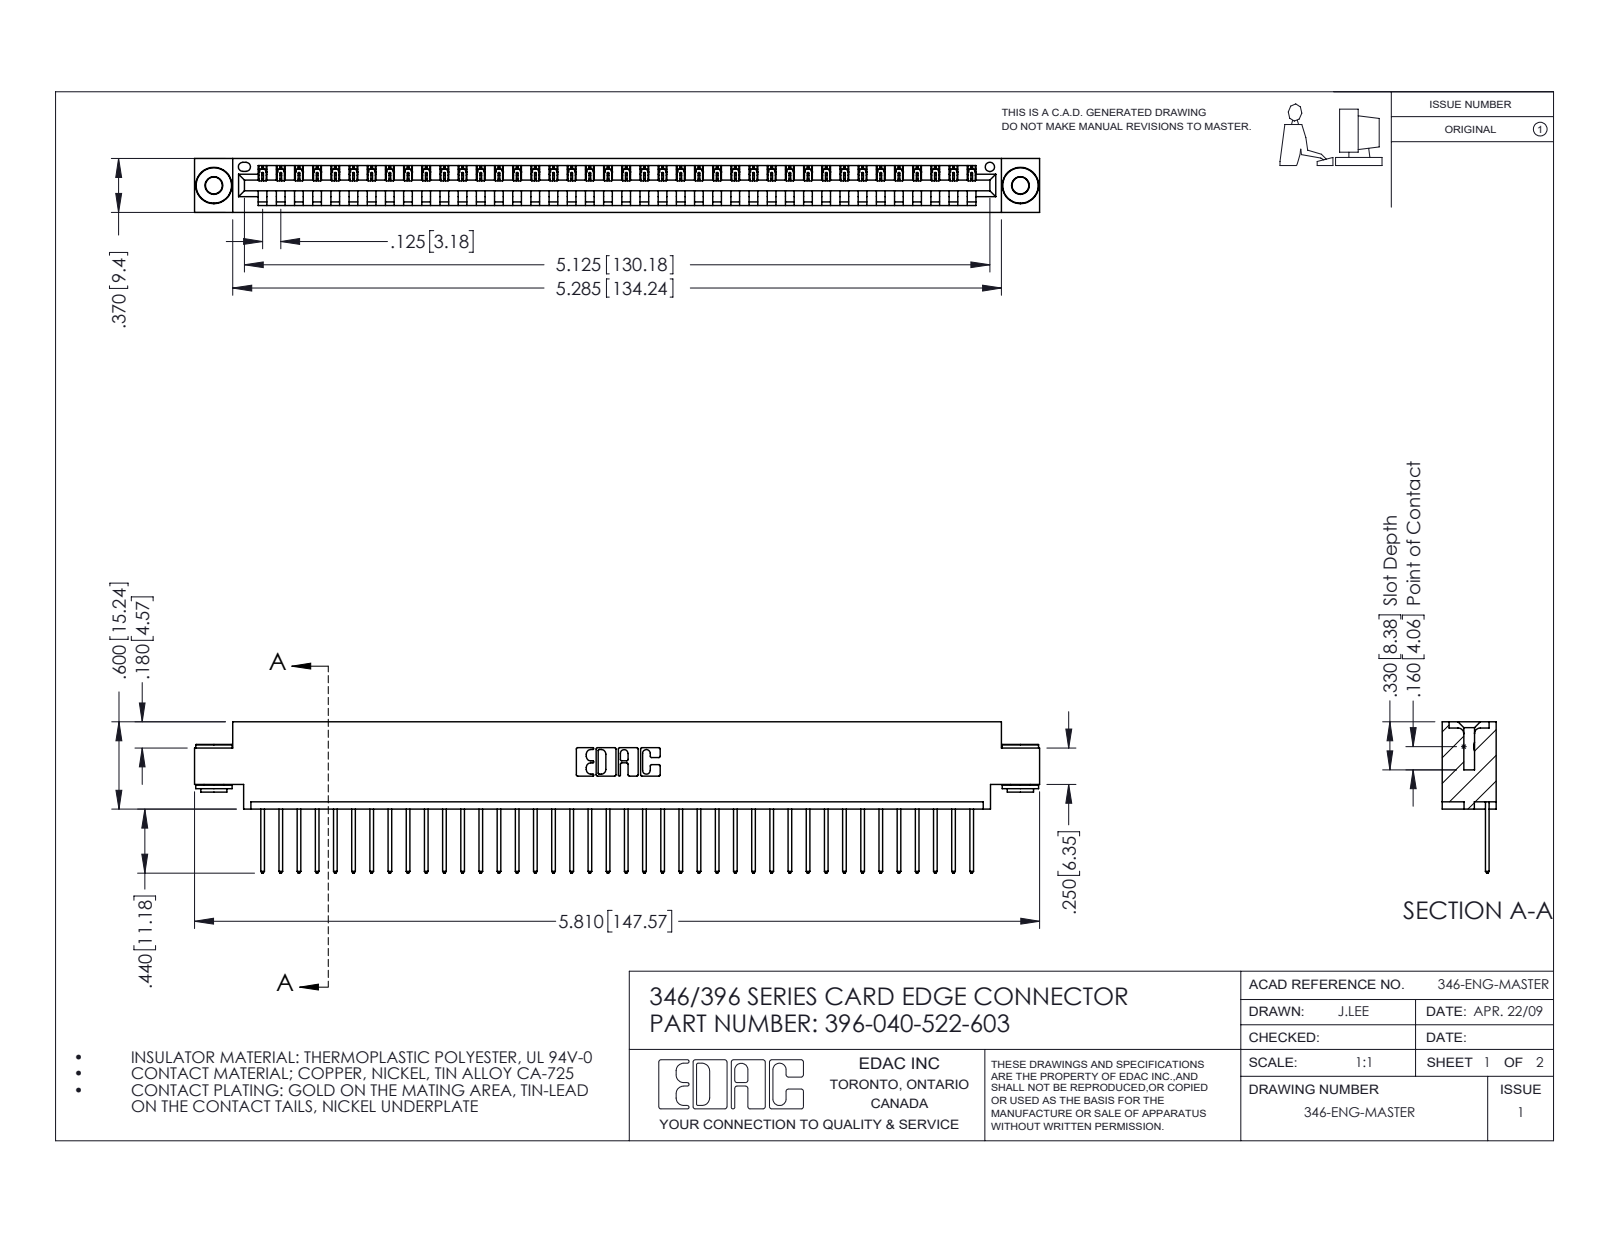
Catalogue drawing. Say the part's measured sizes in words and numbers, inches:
The part is named "396-040-522-603; 345-292-001_345-293-122; 346 Part_0.170 Offset - 0.156 Dia-TH; 345-250-002_345-250-002-102". Its 3-D file was written by "SolidWorks 2016 (CONFIG_CONTROL_DESIGN)". It is 43 solids with 2484 faces: 1690 planar, 786 cylindrical and 8 other. Overall it measures 5.81 by 1.04 by 0.37 inches. Its volume is 0.853 cubic inches and its surface area 27.87 square inches. Round holes: 2 of diameter 0.116, 2 of diameter 0.156, 1 of diameter 0.064. Round bosses or shafts: 2 of diameter 0.25, 2 of diameter 0.18, 2 of diameter 0.136. Partial cylindrical surfaces (rounded edges, fillets, slot ends): 80 of radius 0.006, 80 of radius 0.01, 22 of radius 0.01, 6 of radius 0.007, 6 of radius 0.031, 3 of radius 0.026, 2 of radius 0.031, 2 of radius 0.04. The main face-to-face distances are 0.048, 0.322, 0.37, 0.25, 0.025, 0.072, 0.298, 0.148, 0.222, 0.1. The hole center spacings are 0.246, 5.336, 5.545.
